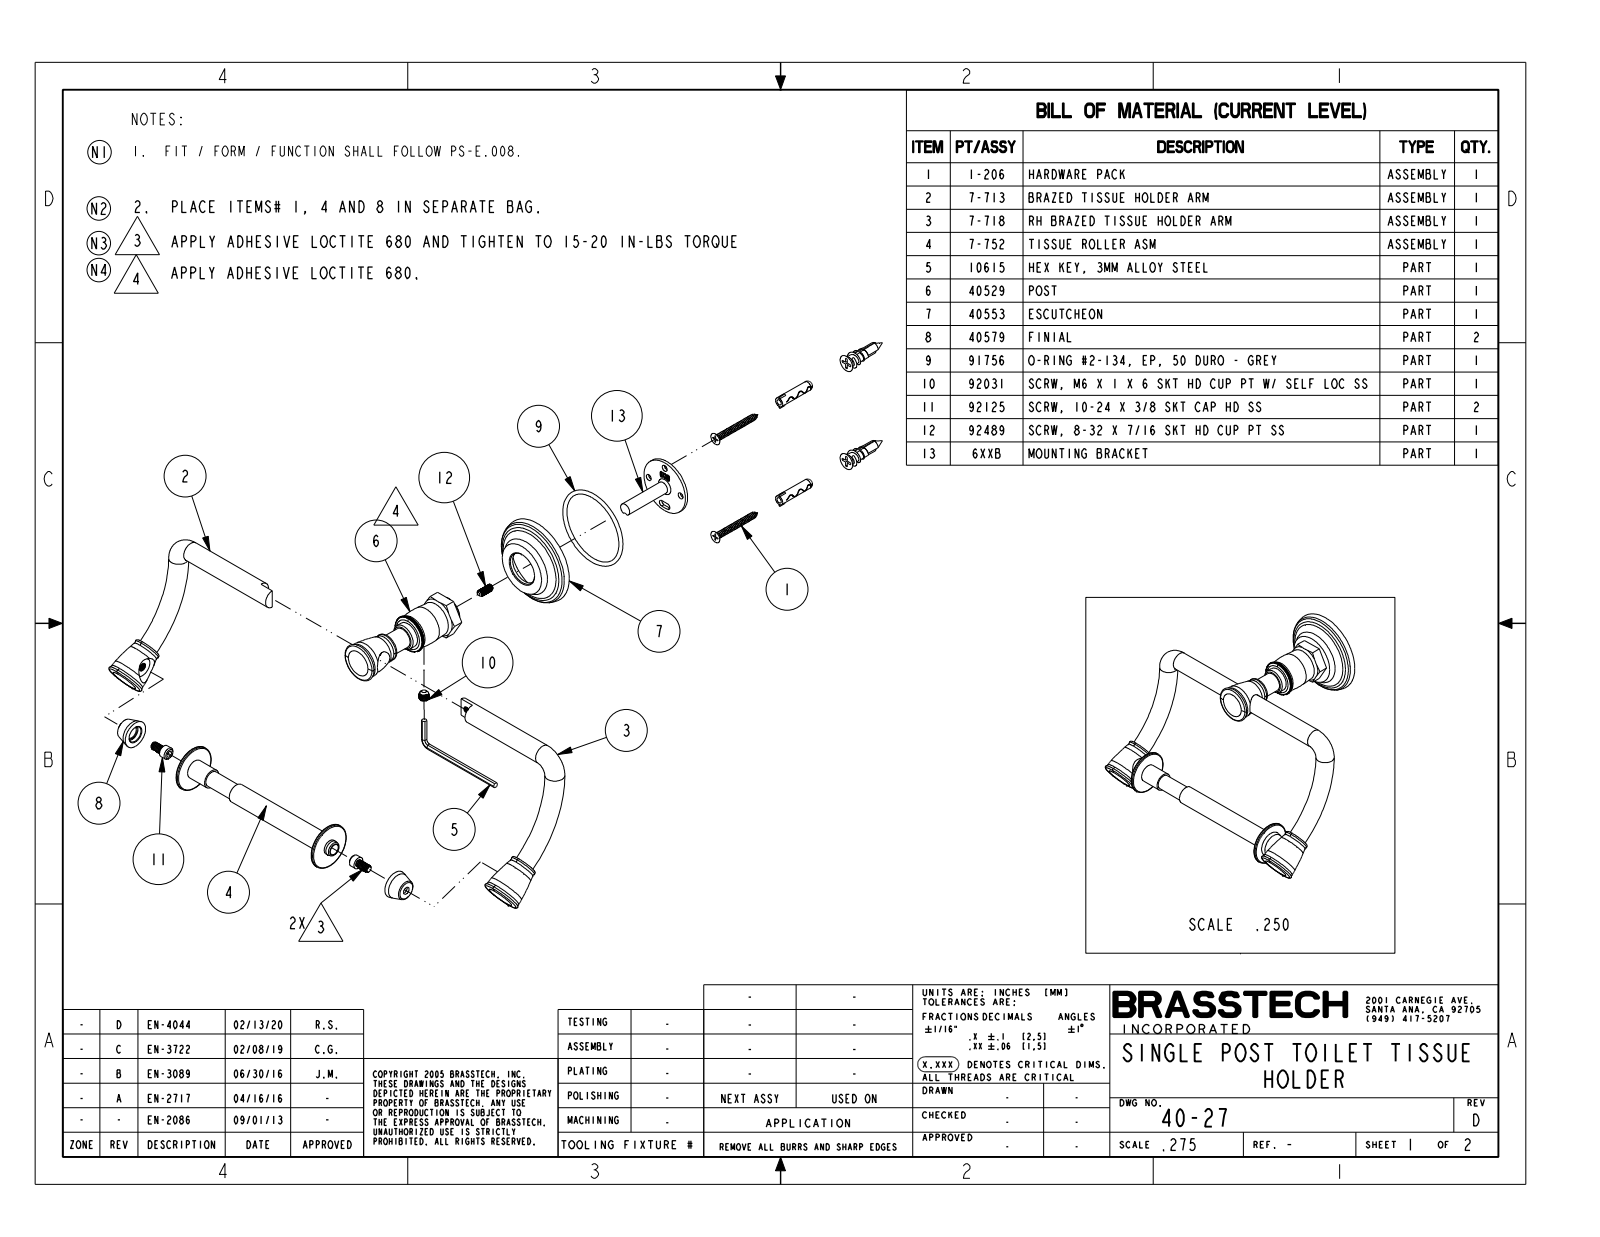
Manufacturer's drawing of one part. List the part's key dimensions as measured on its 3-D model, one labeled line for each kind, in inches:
Part name (STEP PRODUCT): 40553; 6XXB; 40529; 92031 (+8 more)
STEP written by: PRO/ENGINEER BY PARAMETRIC TECHNOLOGY CORPORATION, 2013150 (CONFIG_CONTROL_DESIGN)
Units: inches
Bodies: 18 solids, 1233 faces (436 planar, 299 cylindrical, 498 other)
Overall size (bounding box): 7.254 × 5.351 × 4.726
Volume: 6.148 in³ · Surface area: 160 in²
Round holes (diameter × count): ⌀0.169 ×3, ⌀0.172 ×2, ⌀0.306 ×2, ⌀0.506 ×2, ⌀0.136 ×1, ⌀0.15 ×1, ⌀0.197 ×1, ⌀0.198 ×1, ⌀0.32 ×1, ⌀0.33 ×1, ⌀0.52 ×1, ⌀0.585 ×1
Round bosses / shafts (diameter × count): ⌀0.14 ×12, ⌀0.204 ×4, ⌀0.5 ×3, ⌀0.3 ×2, ⌀0.27 ×2, ⌀1.9 ×1, ⌀1.46 ×1, ⌀0.825 ×1
Partial cylindrical surfaces — rounded edges, fillets, slot ends (radius × count): R0.07 ×2, R0.085 ×2, R0.102 ×2, R0.158 ×1, R1.214 ×1, R1.786 ×1
Main face-to-face distances: 0.08, 0.534, 0.454, 0.99, 0.1, 0.085, 0.449, 0.434, 0.354, 0.349
Hole centre spacings: 0.563, 0.796, 0.562, 0.564, 1.126, 3.263, 6.259
